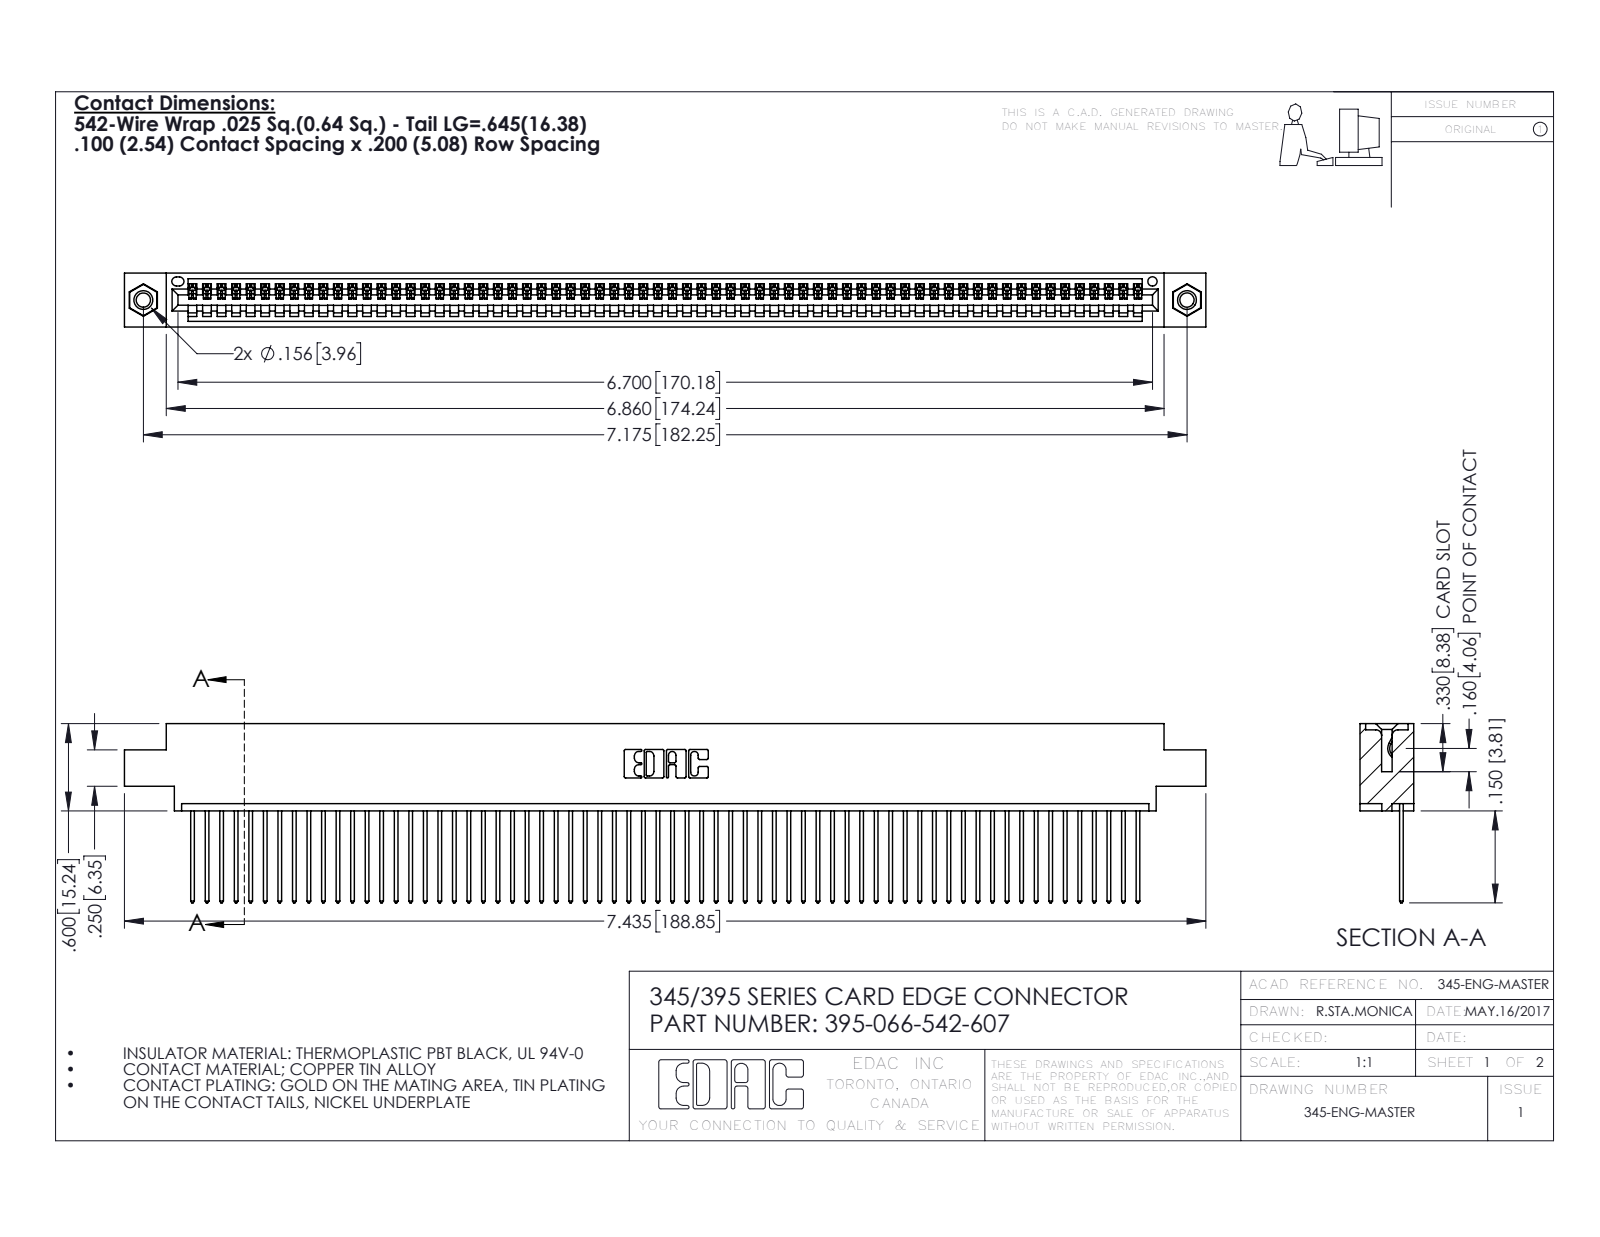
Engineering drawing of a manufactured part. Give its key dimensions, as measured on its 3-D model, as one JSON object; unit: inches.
{"part_name": "395-066-542-607; 345-250-001_345-250-005-103; 345-292-001_345-293-142; 345 Part_0.170 Offset - 0.156 Dia-TI", "step_written_by": "SolidWorks 2016 (CONFIG_CONTROL_DESIGN)", "units": "inches", "bodies": {"solids": 69, "faces": 4018, "planar": 2756, "cylindrical": 1246, "other": 16}, "overall_size": [7.435, 1.232, 0.37], "volume_in3": 1.108, "surface_area_in2": 39.58, "round_holes": [[0.098, 2], [0.125, 2], [0.156, 2], [0.064, 1]], "round_bosses_or_shafts": [[0.155, 2]], "partial_cylinders_radius": [[0.006, 132], [0.01, 132], [0.01, 22], [0.007, 6], [0.031, 6], [0.026, 3], [0.031, 2], [0.04, 2]], "face_to_face_distances": [0.072, 0.298, 0.37, 0.098, 0.272, 0.025, 0.2, 0.225, 0.175, 0.149], "hole_center_spacings": [0.27, 6.939, 7.175]}
